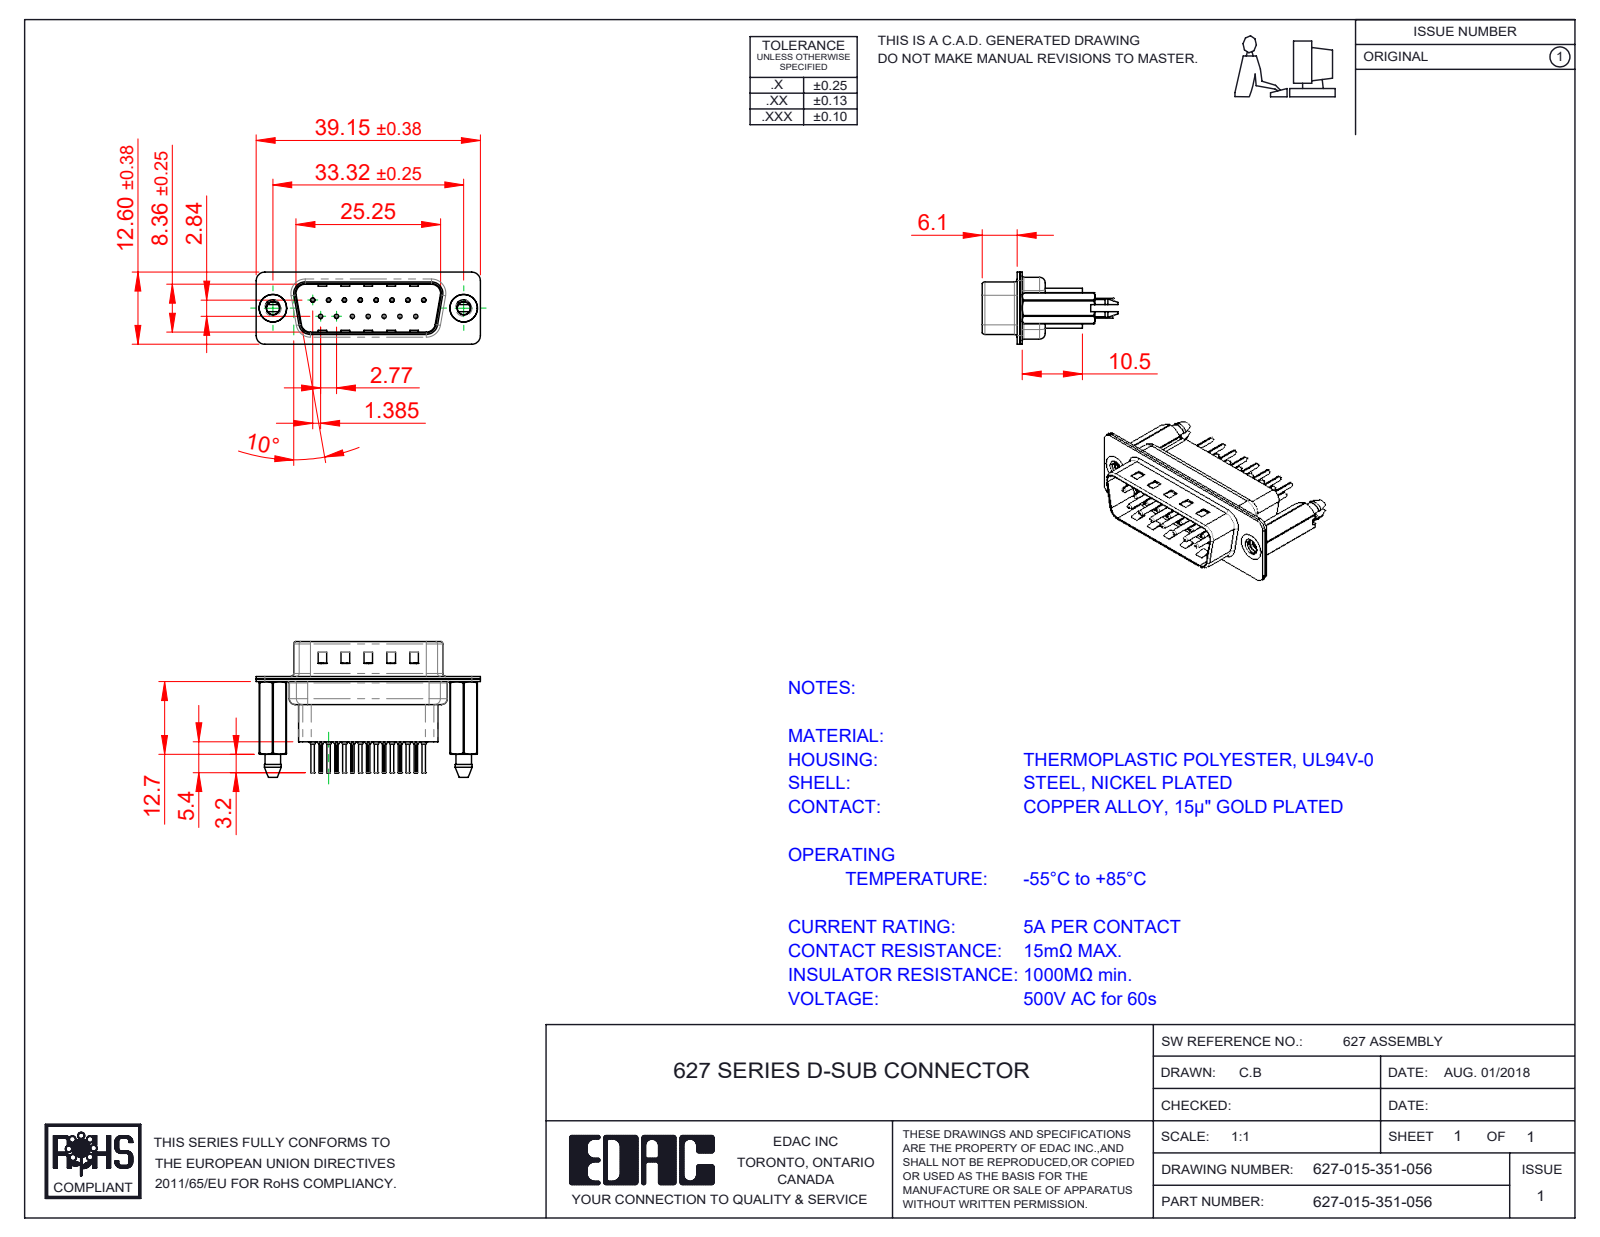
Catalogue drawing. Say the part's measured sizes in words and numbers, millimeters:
The part is named "627 Contact Row 2_41; 627-015-351-056; 627 Shell Rear_15 Contacts; 627 Shell Front_15 Contacts (+3 more)". Its 3-D file was written by "SolidWorks 2020 (CONFIG_CONTROL_DESIGN)". It is 20 solids with 1918 faces: 531 planar, 754 cylindrical and 633 other. Overall it measures 39.15 by 23.6 by 12.6 millimeters. Its volume is 2 858 cubic millimeters and its surface area 7 369 square millimeters. Round holes: 15 of diameter 0.2, 15 of diameter 0.35, 15 of diameter 1.1, 15 of diameter 1.6, 2 of diameter 2.26, 2 of diameter 4, 2 of diameter 4.8. Round bosses or shafts: 15 of diameter 2, 15 of diameter 1.5, 15 of diameter 0.75, 15 of diameter 0.6, 2 of diameter 4.9. Partial cylindrical surfaces (rounded edges, fillets, slot ends): 30 of radius 0.1, 18 of radius 1.5, 12 of radius 2, 10 of radius 1.6, 8 of radius 0.5, 4 of radius 0.25, 4 of radius 0.6, 4 of radius 0.65. The main face-to-face distances are 0.4, 0.45, 0.9, 0.82, 9.58, 1.5, 0.68, 7.68, 4.76, 1.4. The hole center spacings are 3.16, 2.77, 5.54, 8.31, 11.08, 5.03, 5.04, 7.48.
